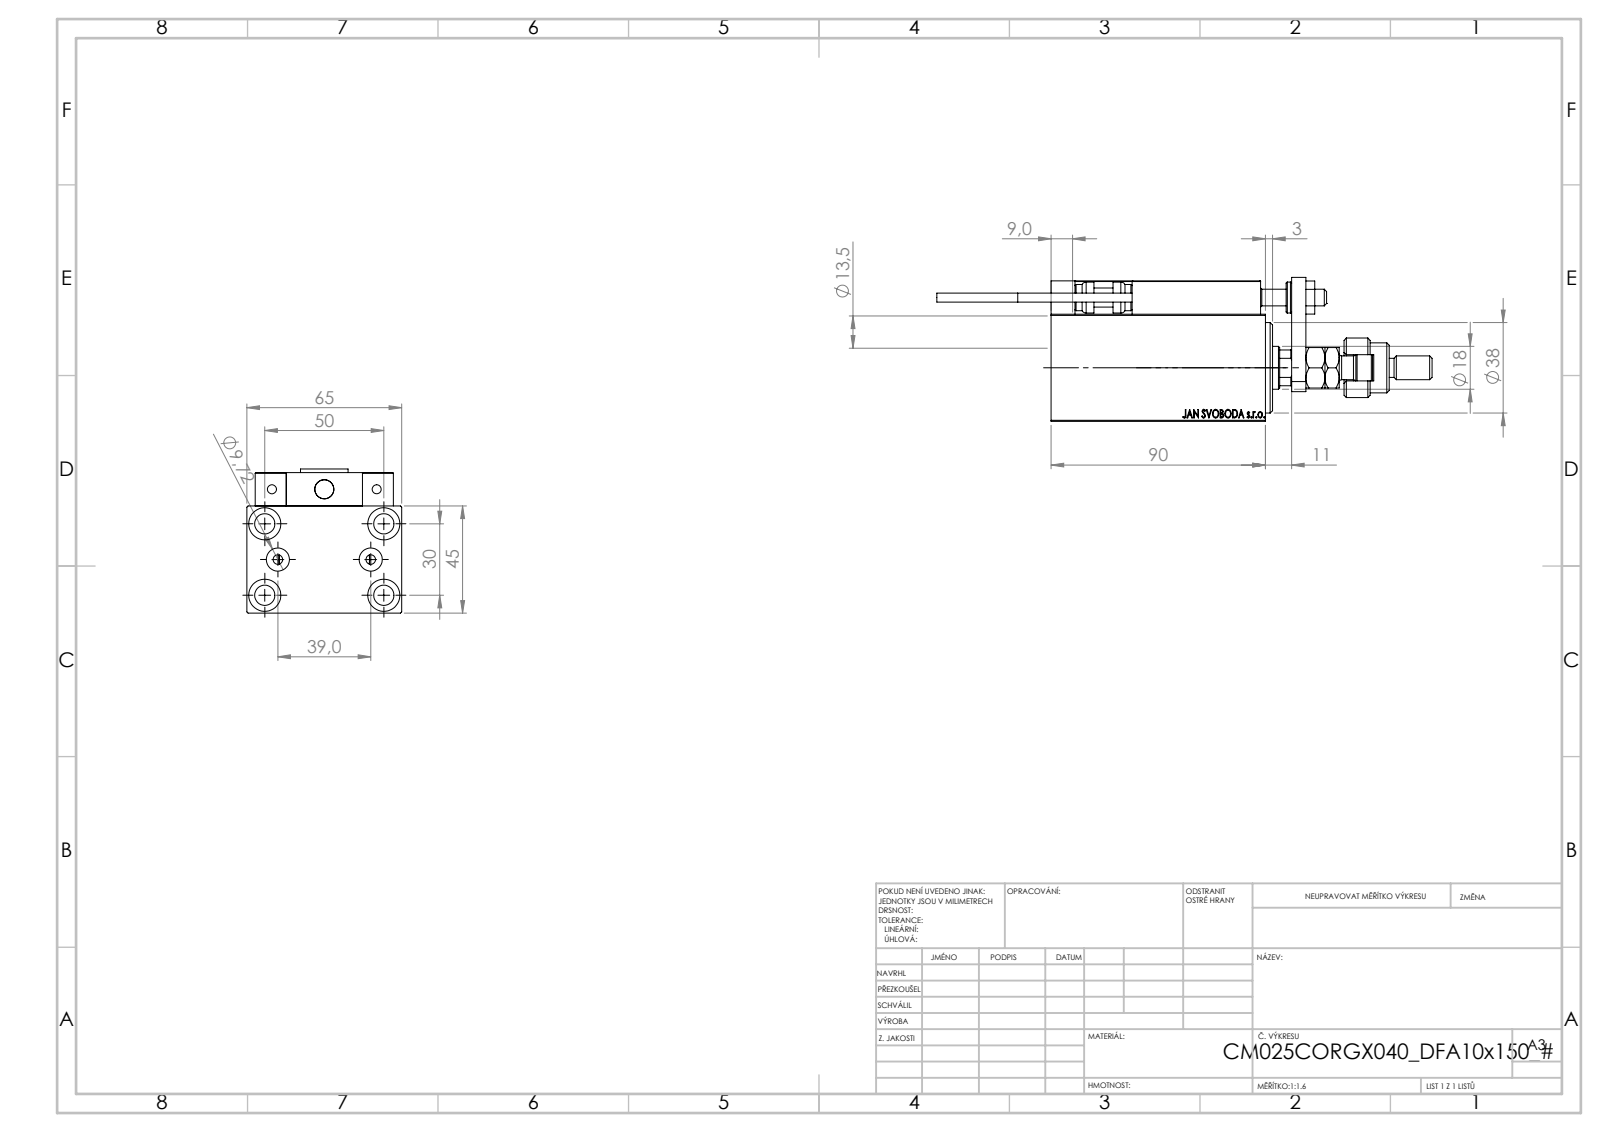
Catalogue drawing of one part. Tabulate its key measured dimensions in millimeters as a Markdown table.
| quantity | value |
| --- | --- |
| part name | ALLEN BOLT D5; NUT_D12; V450CM_C_VCP; MAGNET (+7 more) |
| STEP written by | SolidWorks 2019 (CONFIG_CONTROL_DESIGN) |
| units | millimeters |
| bodies | 25 solids, 1363 faces (588 planar, 197 cylindrical, 578 other) |
| overall size | 208 × 65 × 60.5 |
| volume | 285 513 mm³ |
| surface area | 85 625 mm² |
| round holes (diameter × count) | 4 × 6, 8 × 5, 8.5 × 5, 3.2 × 4, 13.5 × 4, 5 × 2, 9.72 × 2, 7 × 1, 14.5 × 1, 18 × 1, 21.5 × 1, 27 × 1 |
| round bosses / shafts (diameter × count) | 5 × 2, 3.8 × 2, 25 × 1, 21 × 1, 16 × 1, 13 × 1, 11 × 1, 10 × 1 |
| partial cylindrical surfaces (radius × count) | 0.3 × 30, 3 × 2, 5.5 × 1, 8.5 × 1, 8.75 × 1 |
| main face-to-face distances | 45, 65, 14, 6, 59, 3, 101, 7, 5, 19 |
| hole center spacings | 15.98, 29.15, 46.96, 11.37, 19.5, 20, 28.9, 29.59 |
